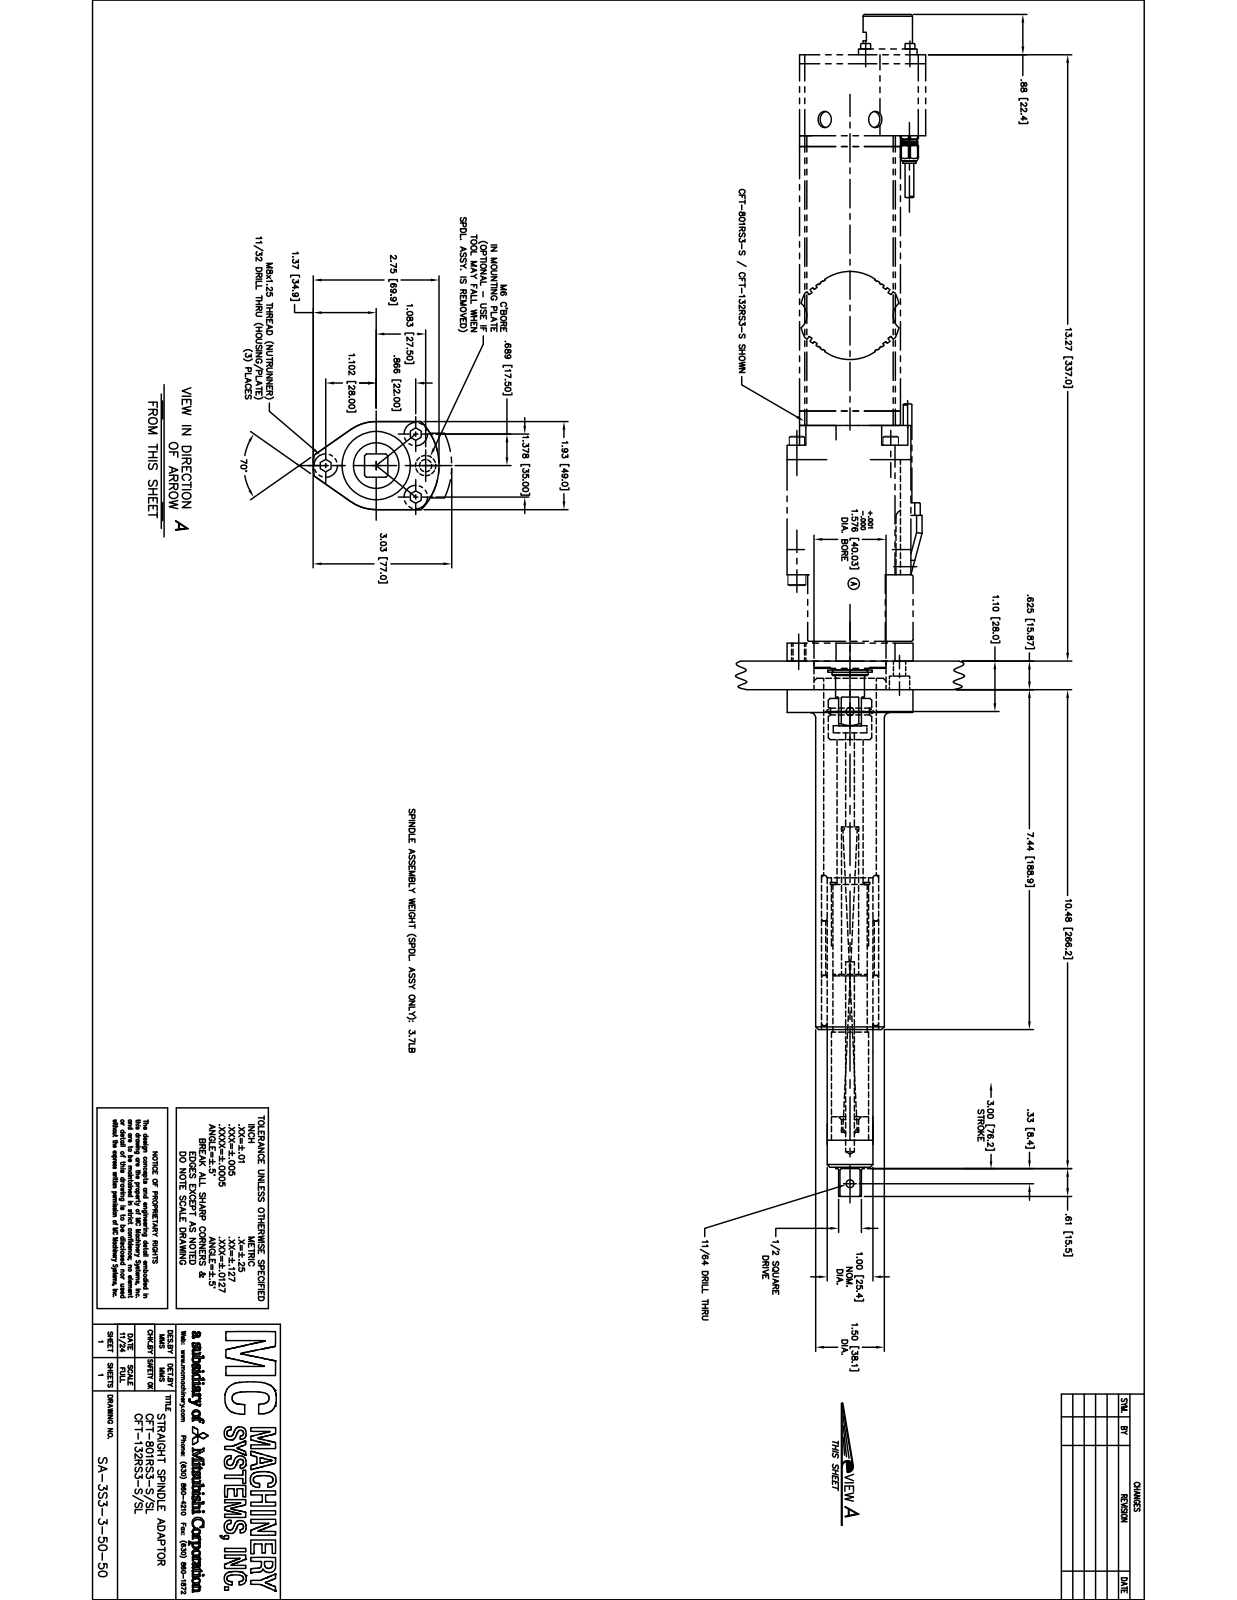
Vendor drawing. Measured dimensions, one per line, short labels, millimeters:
name: SA-3S3-3-50-50; SCE-1614P-3; S-10-5.74-30-07; SCE-1614P (+8 more)
written by: SolidWorks 2017 (CONFIG_CONTROL_DESIGN)
unit: mm
bodies: 17 solids, 302 faces (104 planar, 116 cylindrical, 82 other)
size: 263.1 × 69.9 × 48.8
volume: 177 600 mm³; area: 115 700 mm²
holes: 3× ⌀9, 1× ⌀2.4, 1× ⌀3.2, 1× ⌀4.4, 1× ⌀4.7, 1× ⌀4.7, 1× ⌀9.5, 1× ⌀9.7, 1× ⌀18, 1× ⌀20.6, 1× ⌀21.5, 1× ⌀21.9
bosses: 4× ⌀2.2, 1× ⌀40, 1× ⌀38.1, 1× ⌀31.8, 1× ⌀25.4, 1× ⌀24.1, 1× ⌀21.6, 1× ⌀20.7
rounds: 4× R0.8, 1× R8.5, 1× R24.4, 1× R34.9
face distances: 12.6, 1, 12.8, 31, 24.4, 55.4, 12.7, 58, 27.1, 82.4
hole spacings: 28.1, 53, 28, 35, 237.7
